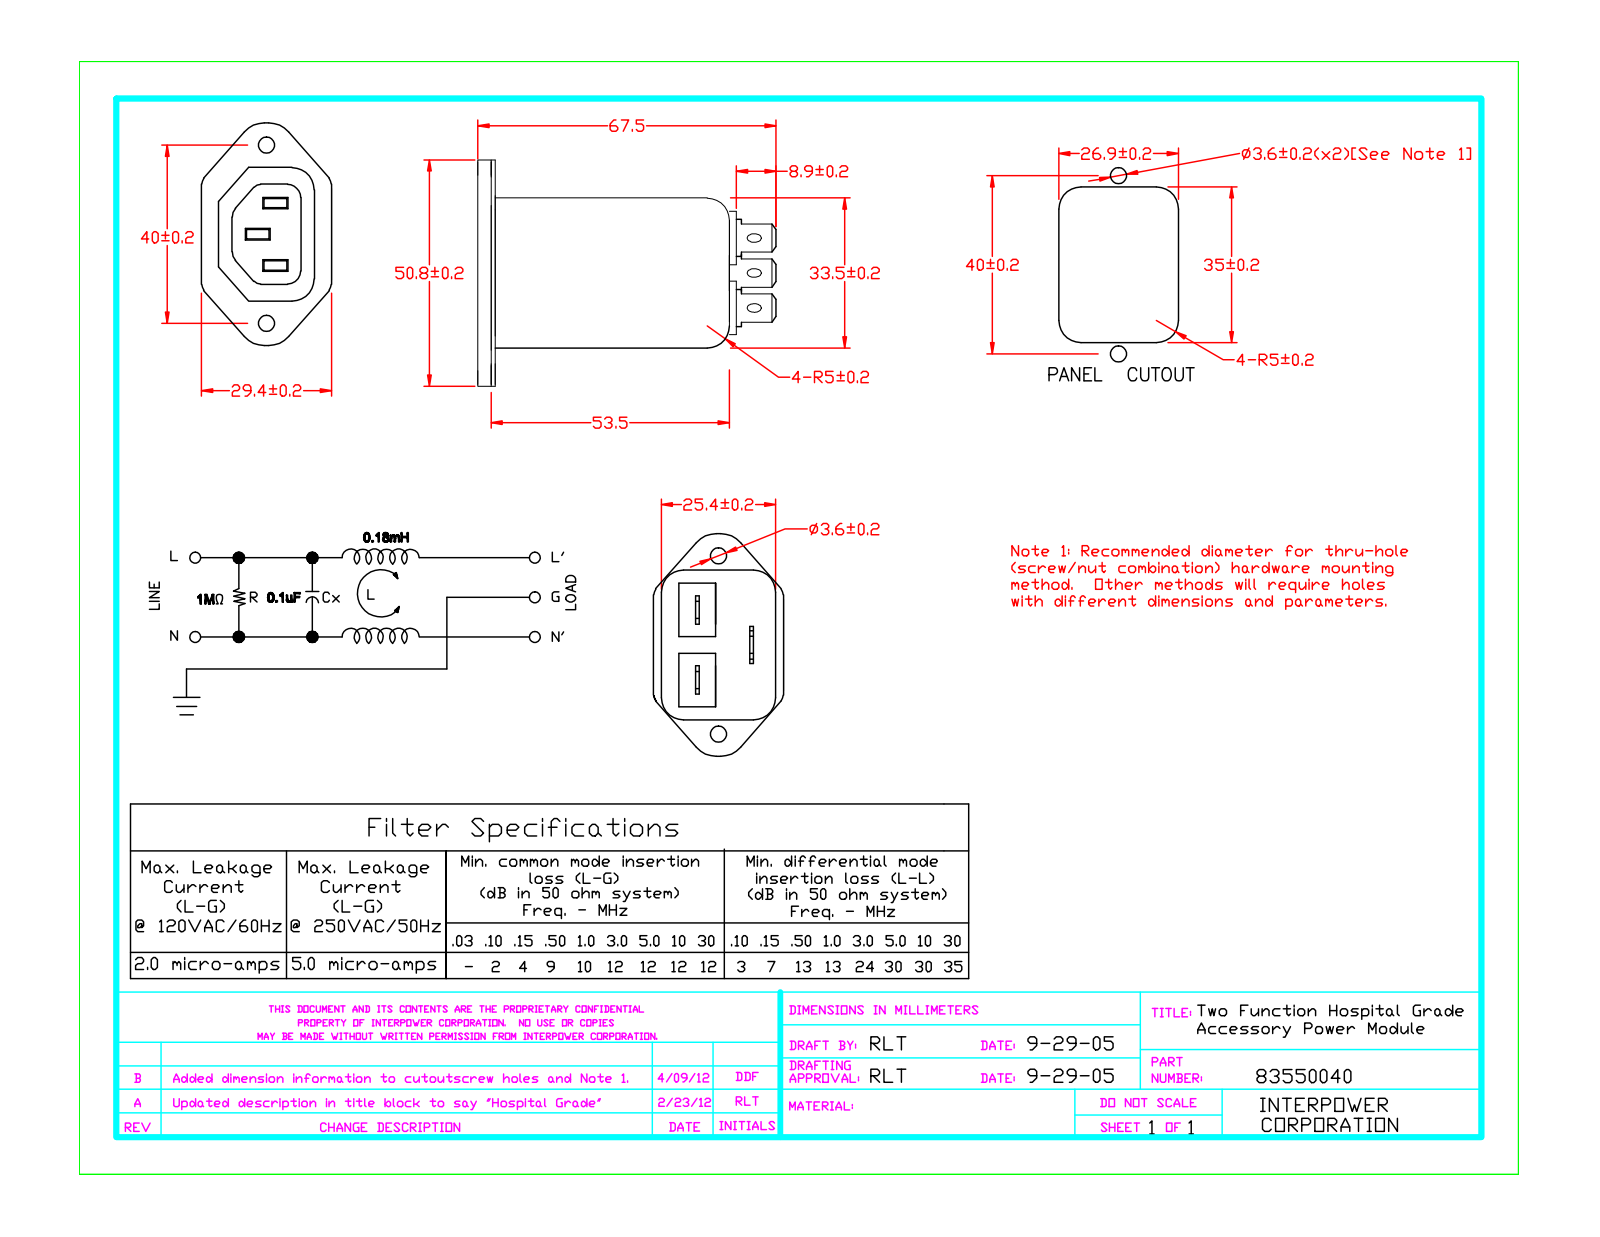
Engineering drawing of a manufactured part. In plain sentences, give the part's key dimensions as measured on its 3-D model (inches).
The part is named "83550040". Its 3-D file was written by "SolidWorks 2007 (CONFIG_CONTROL_DESIGN)". It is 1 solid with 179 faces: 95 planar, 58 cylindrical and 26 other. Overall it measures 2.657 by 2 by 1.157 inches. Its volume is 2.604 cubic inches and its surface area 21.15 square inches. Round holes: 2 of diameter 0.136. Partial cylindrical surfaces (rounded edges, fillets, slot ends): 12 of radius 0.01, 8 of radius 0.118, 6 of radius 0.079, 6 of radius 0.197, 4 of radius 0.039, 2 of radius 0.236. The main face-to-face distances are 1, 1.319, 0.073, 0.927, 0.276, 0.126, 0.083, 0.124, 0.069, 1.25. The hole center spacings are 1.575.
